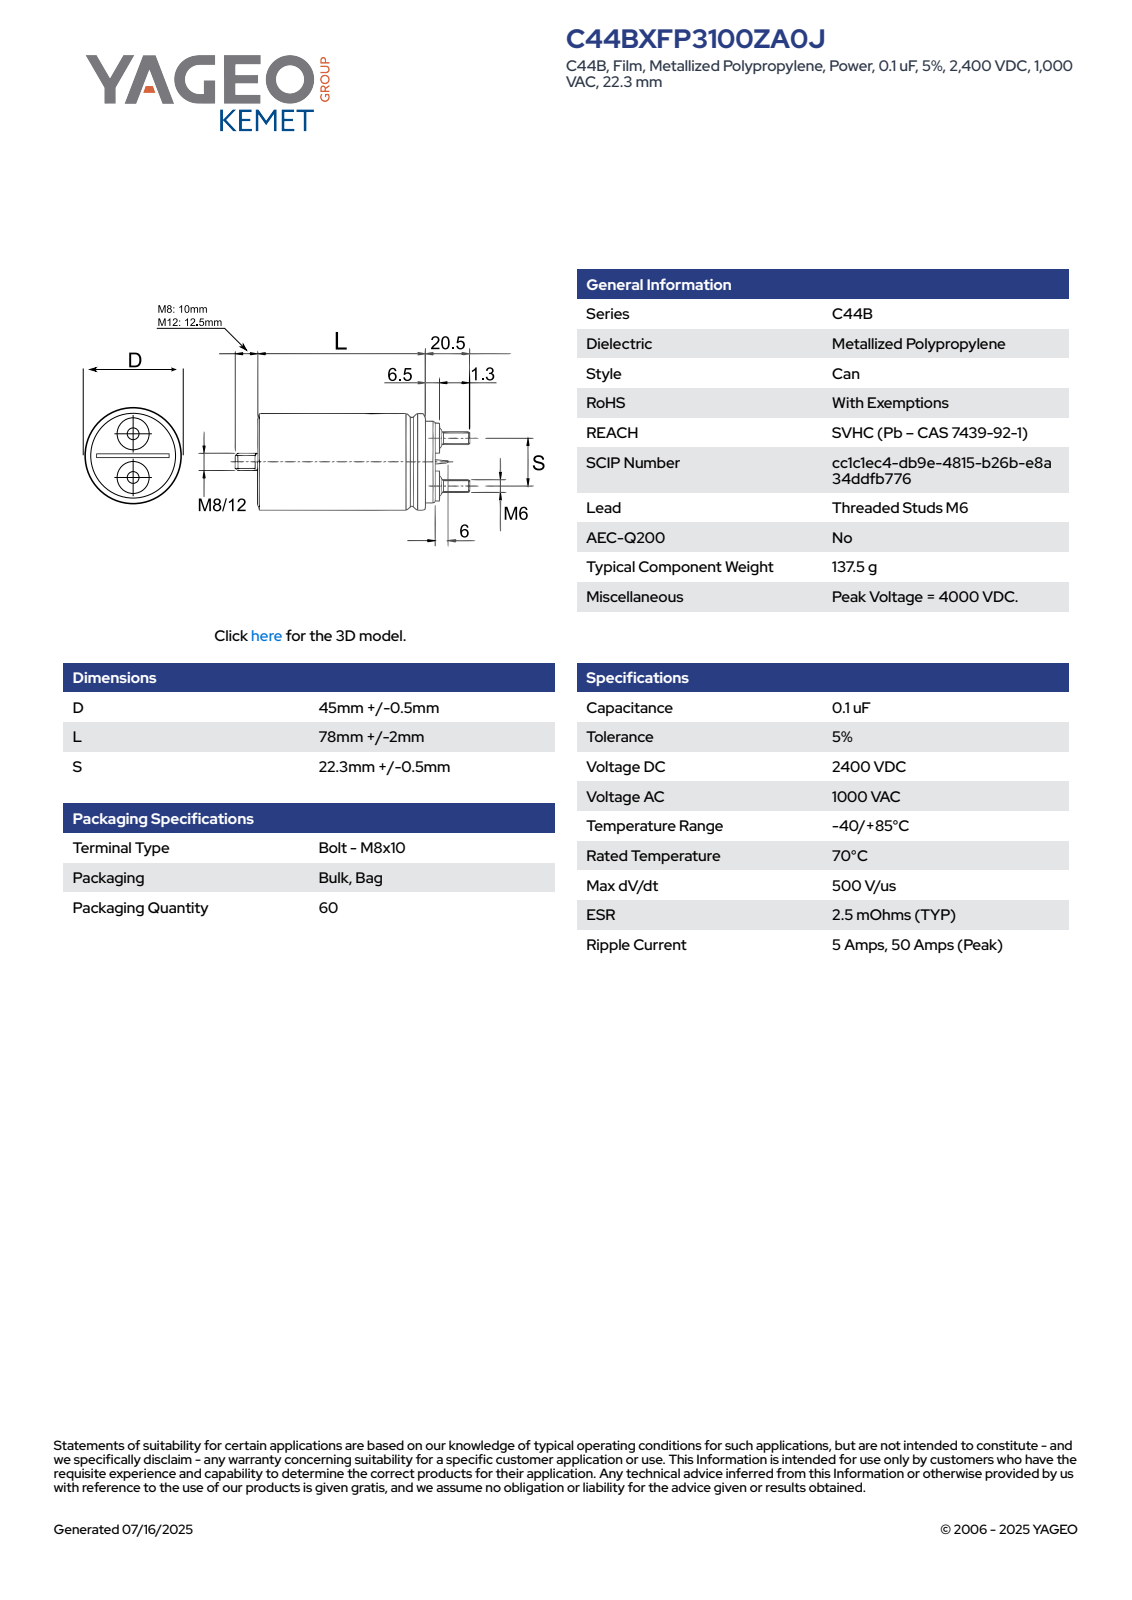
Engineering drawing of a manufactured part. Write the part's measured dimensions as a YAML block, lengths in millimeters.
part_name: "CFP_M6_45X78_D45.5L80S22.8"
step_written_by: "SolidWorks 2014 (AUTOMOTIVE_DESIGN)"
units: millimeters
bodies: {solids: 1, faces: 117, planar: 35, cylindrical: 39, other: 43}
overall_size: [112.5, 45.51, 45.5]
volume: 135269
surface_area: 17035
round_bosses_or_shafts:
  - {diameter: 12.5, count: 2}
  - {diameter: 9.03, count: 2}
  - {diameter: 6, count: 2}
  - {diameter: 45.5, count: 1}
  - {diameter: 40.27, count: 1}
  - {diameter: 9, count: 1}
partial_cylinders:
  - {radius: 0.35, count: 1}
  - {radius: 22.76, count: 1}
face_to_face_distances: [84, 80, 4, 0.7, 86.5, 6.5, 2.5, 87.5, 7.5, 3.5]
